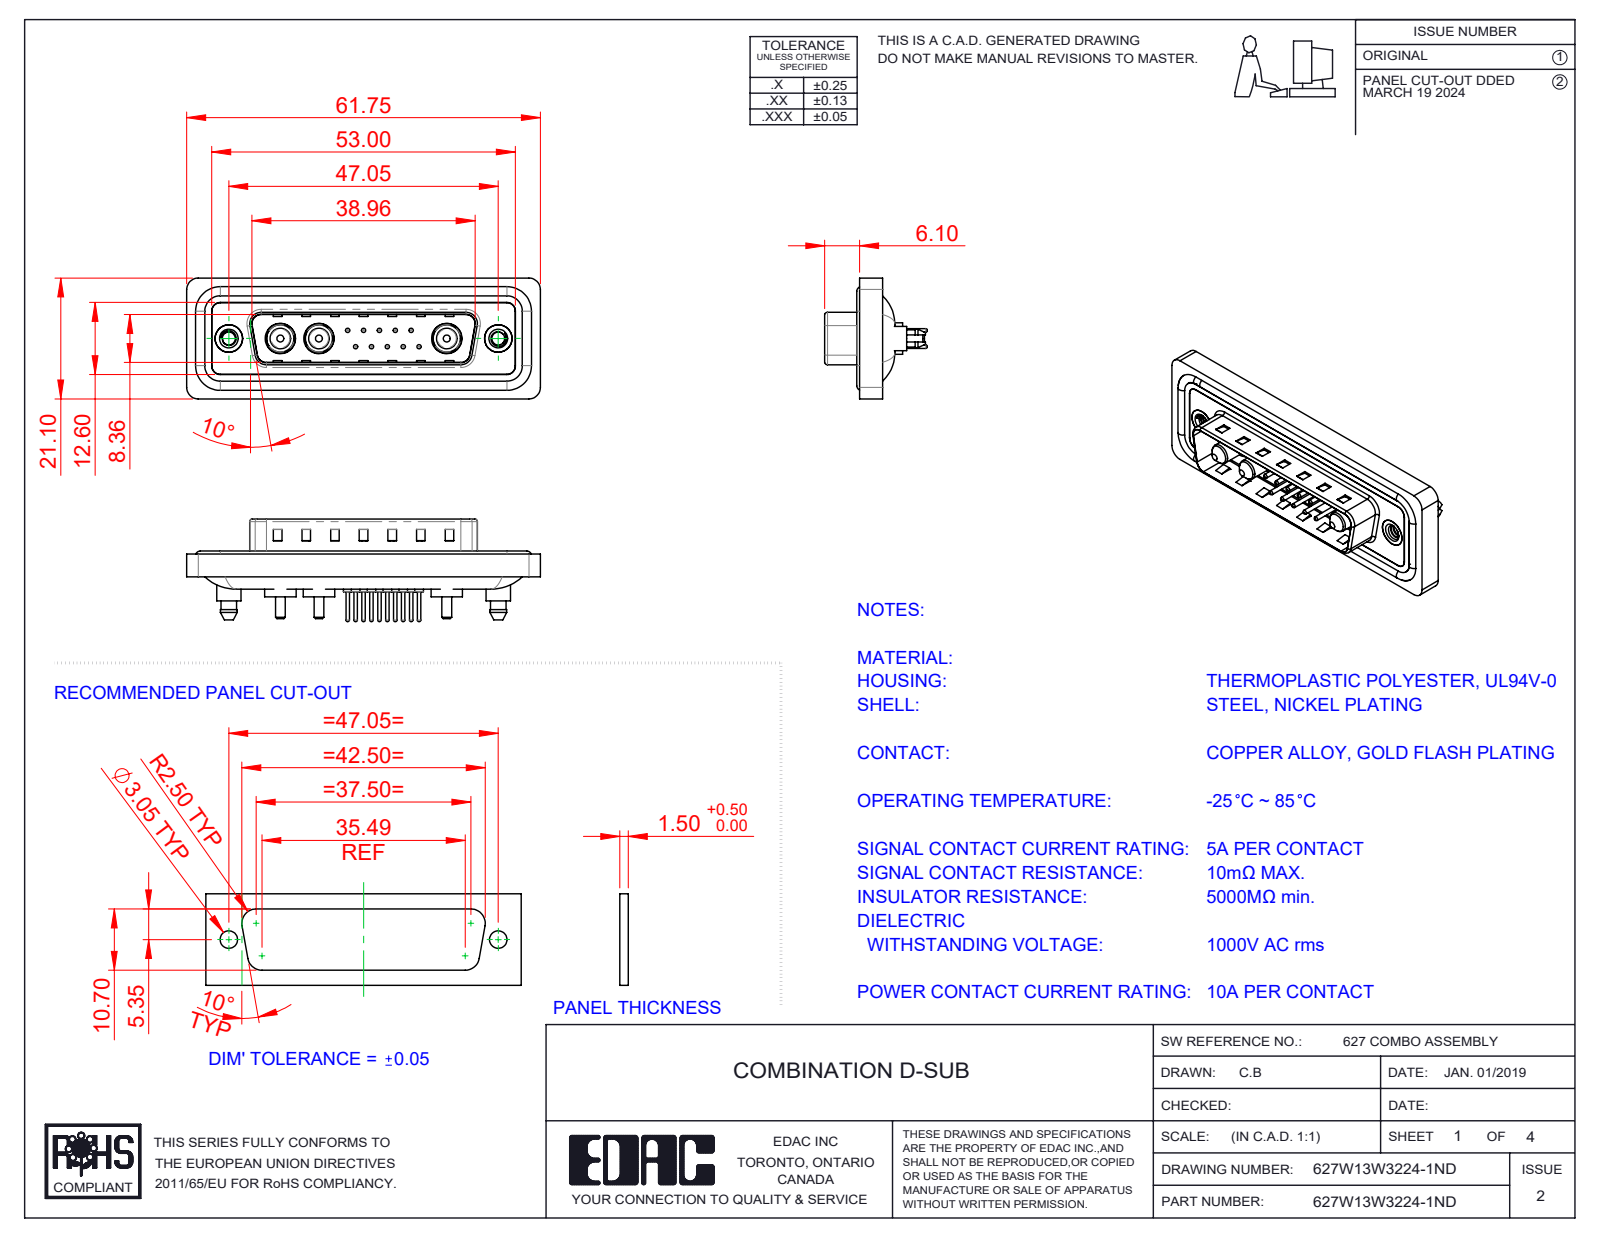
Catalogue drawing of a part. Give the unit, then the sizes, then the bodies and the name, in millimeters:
Units: millimetres
Overall size (bounding box): 61.75 × 21.1 × 17.9
Round holes (diameter × count): ⌀0.75 ×10, ⌀1.6 ×10, ⌀2 ×10, ⌀4.85 ×3, ⌀5.3 ×3, ⌀2.26 ×2, ⌀4 ×2, ⌀4.8 ×2, ⌀5 ×2
Round bosses / shafts (diameter × count): ⌀1.5 ×10, ⌀0.6 ×10, ⌀1.6 ×4, ⌀5.5 ×3, ⌀5.2 ×3, ⌀4.75 ×3, ⌀3.75 ×3, ⌀3.6 ×3
Partial cylindrical surfaces — rounded edges, fillets, slot ends (radius × count): R1.5 ×24, R2 ×18, R1.6 ×10, R0.5 ×8, R0.25 ×4, R0.6 ×4, R0.65 ×4, R0.9 ×4
Main face-to-face distances: 0.4, 1.5, 1.1, 1.6, 0.5, 3.1, 2.9, 0.82, 9.58, 4.1
Hole centre spacings: 3.16, 2.77, 5.04, 5.54, 7.49, 5.03, 8.31, 10.11
Volume: 7 426 mm³ · Surface area: 12 173 mm²
Bodies: 23 solids, 1028 faces (325 planar, 425 cylindrical, 278 other)
Part name (STEP PRODUCT): 627W13W3224-1ND; 627Combo Shell Rear_25 Contacts; 627Combo Threaded Boardlock_D; Power Pin_10A S (+6 more)
STEP written by: SolidWorks 2023 (CONFIG_CONTROL_DESIGN)
